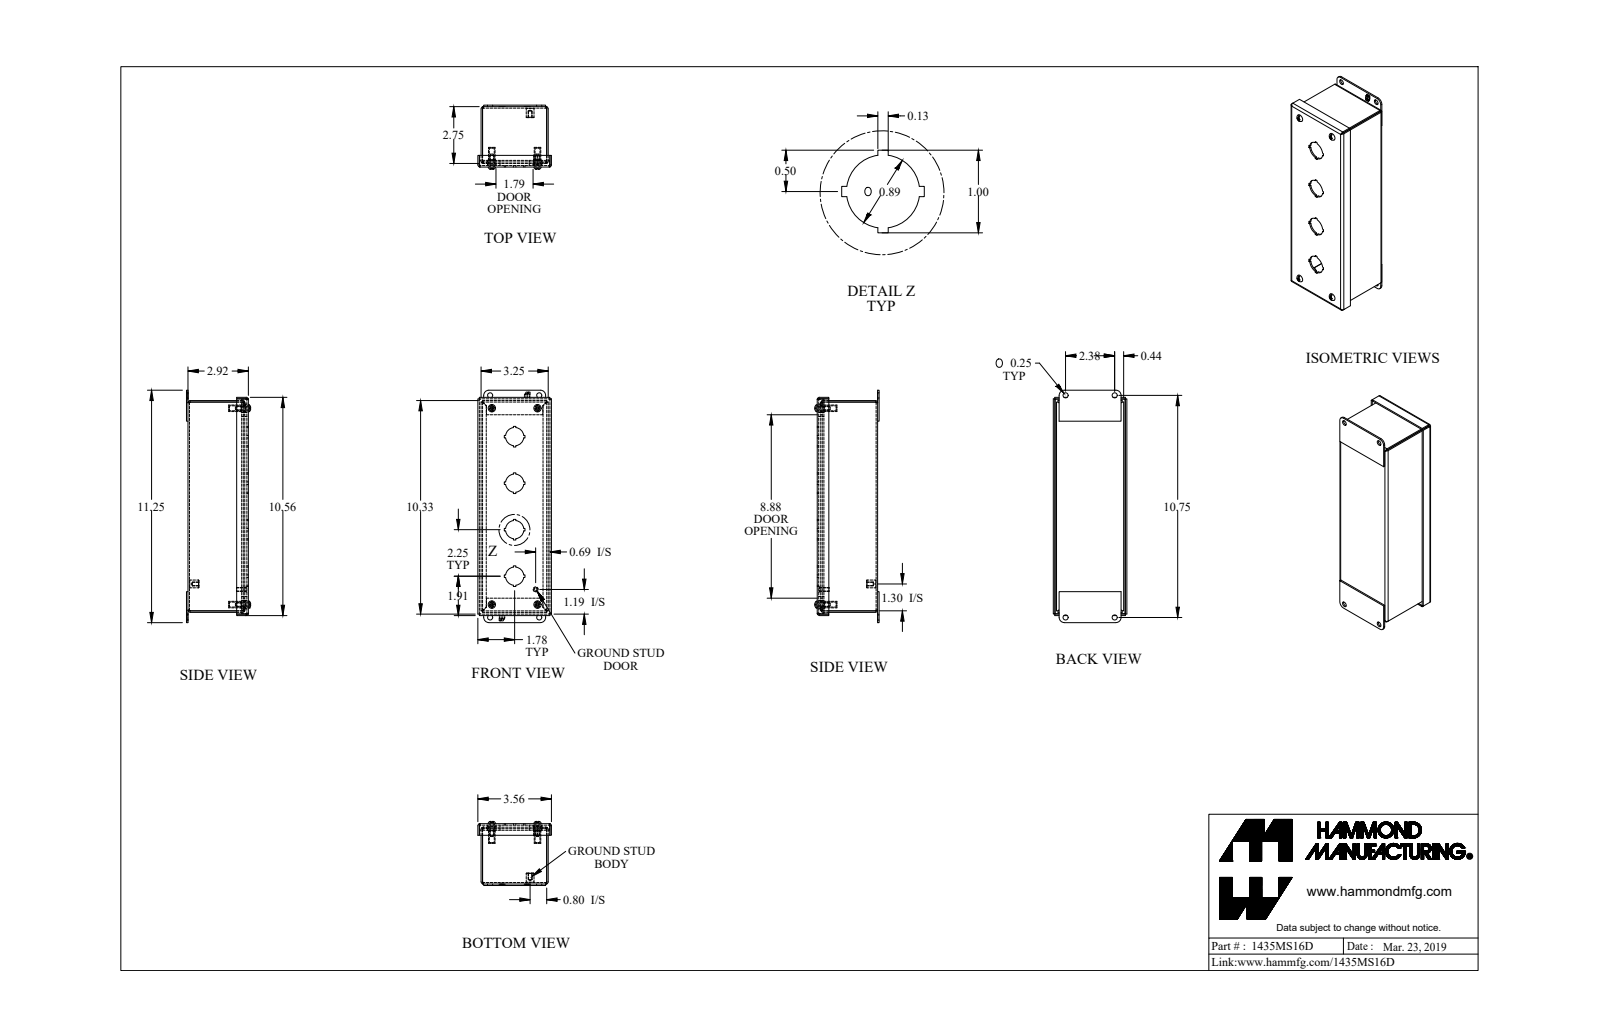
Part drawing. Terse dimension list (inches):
name: 1435MS16D_Default
written by: SolidWorks 2019 (CONFIG_CONTROL_DESIGN)
unit: in
bodies: 19 solids, 509 faces (331 planar, 148 cylindrical, 30 other)
size: 11.25 × 3.562 × 3.104
volume: 14.77 in³; area: 385.7 in²
holes: 8× ⌀0.25, 4× ⌀0.065, 4× ⌀0.239, 4× ⌀0.253, 4× ⌀0.406, 4× ⌀0.886, 1× ⌀0.156
bosses: 5× ⌀0.19, 4× ⌀0.406, 4× ⌀0.315, 4× ⌀0.148, 1× ⌀0.375, 1× ⌀0.25
rounds: 12× R0.036, 12× R0.108, 4× R0.171, 4× R0.25
face distances: 0.072, 2.85, 0.072, 3.178, 2.922, 2.778, 3.25, 3.106, 10.178, 0.156
hole spacings: 8.2, 9.5, 10.126, 10.381, 9.754, 0.63, 0.631, 1.764
